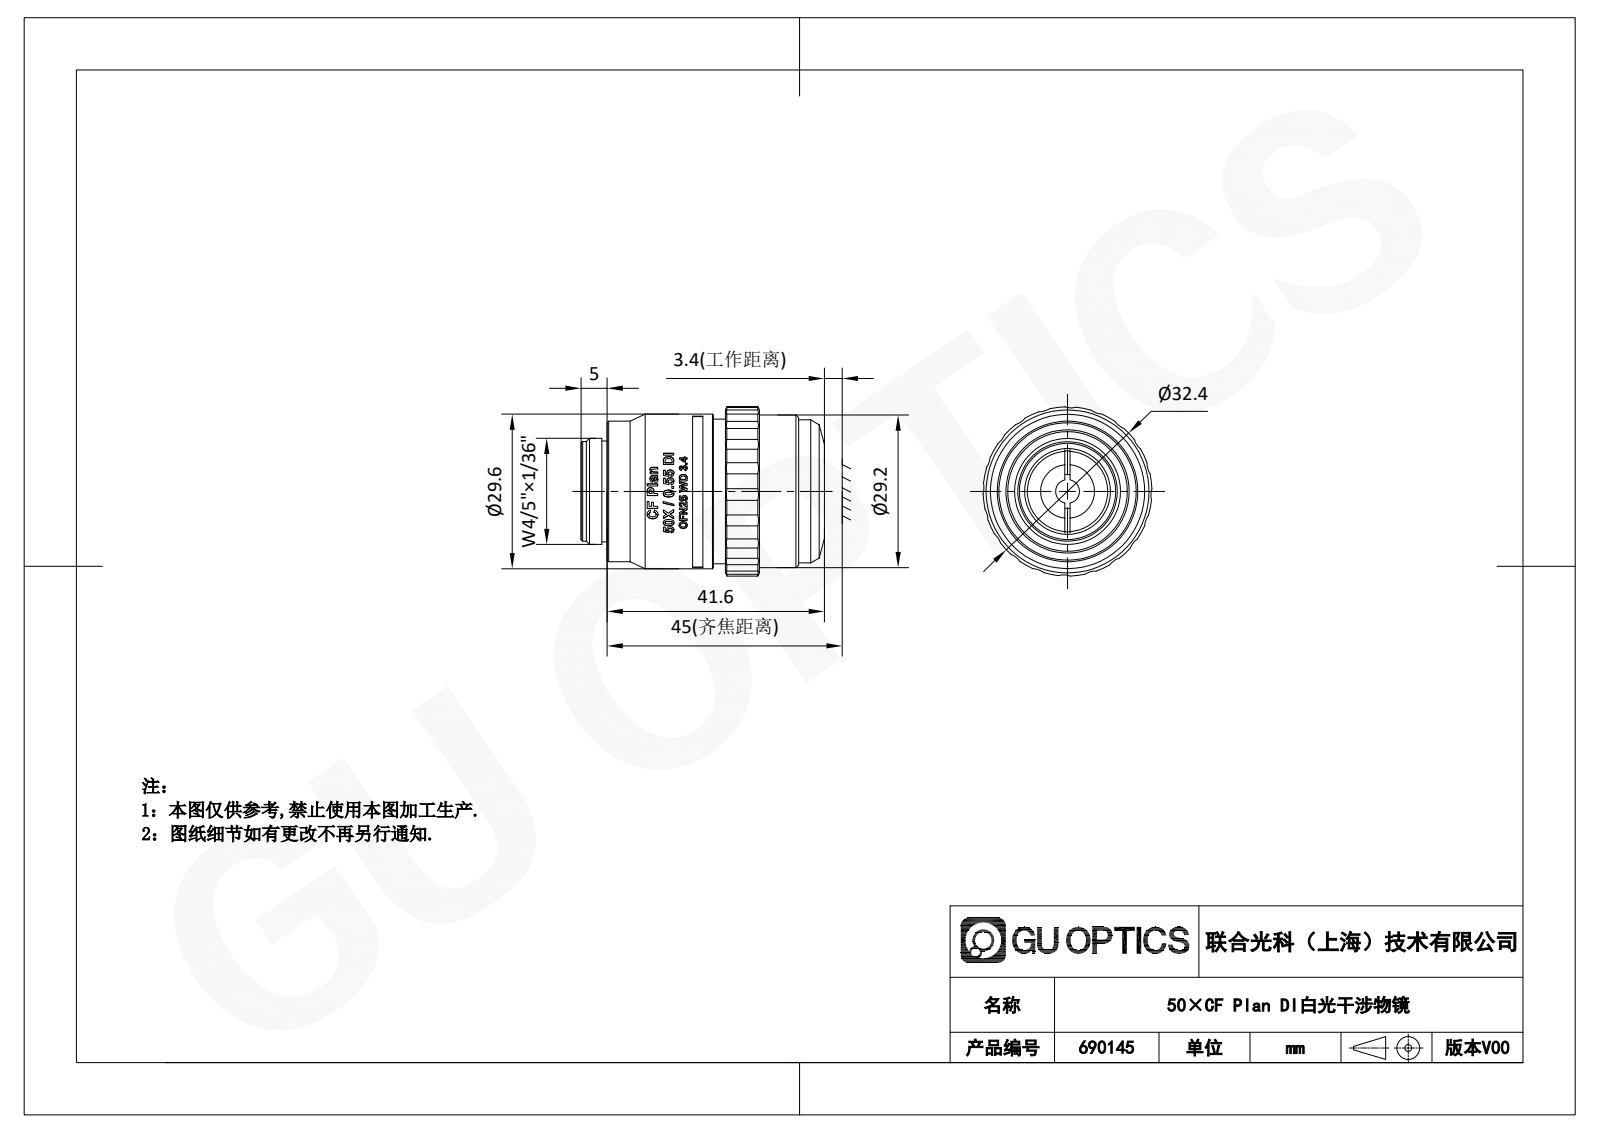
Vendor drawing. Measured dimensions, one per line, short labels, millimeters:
name: X2_524D59165957_X0; X2_88C599705708_X0; X2_540E51499611_X0; X2_7269955C58F3_X0 (+3 more)
written by: SolidWorks 2020 (CONFIG_CONTROL_DESIGN)
unit: mm
bodies: 6 solids, 564 faces (178 planar, 137 cylindrical, 249 other)
size: 46.6 × 32.38 × 32.38
volume: 14 932 mm³; area: 19 800 mm²
holes: 3× ⌀1.57, 2× ⌀1.18, 1× ⌀1.57, 1× ⌀4.6, 1× ⌀12, 1× ⌀15.5, 1× ⌀17.7, 1× ⌀18.4, 1× ⌀20, 1× ⌀20.7, 1× ⌀23.9, 1× ⌀25.4
bosses: 1× ⌀30, 1× ⌀29.6, 1× ⌀29.2, 1× ⌀27.7, 1× ⌀27.4, 1× ⌀27, 1× ⌀26.9, 1× ⌀26.3
rounds: 20× R4, 4× R1.5, 1× R8.41, 1× R14.7, 1× R16.2
face distances: 1, 2, 41.4, 5, 27.65, 26.75, 27.75, 1.5, 40.1, 20.2
hole spacings: 17.1
